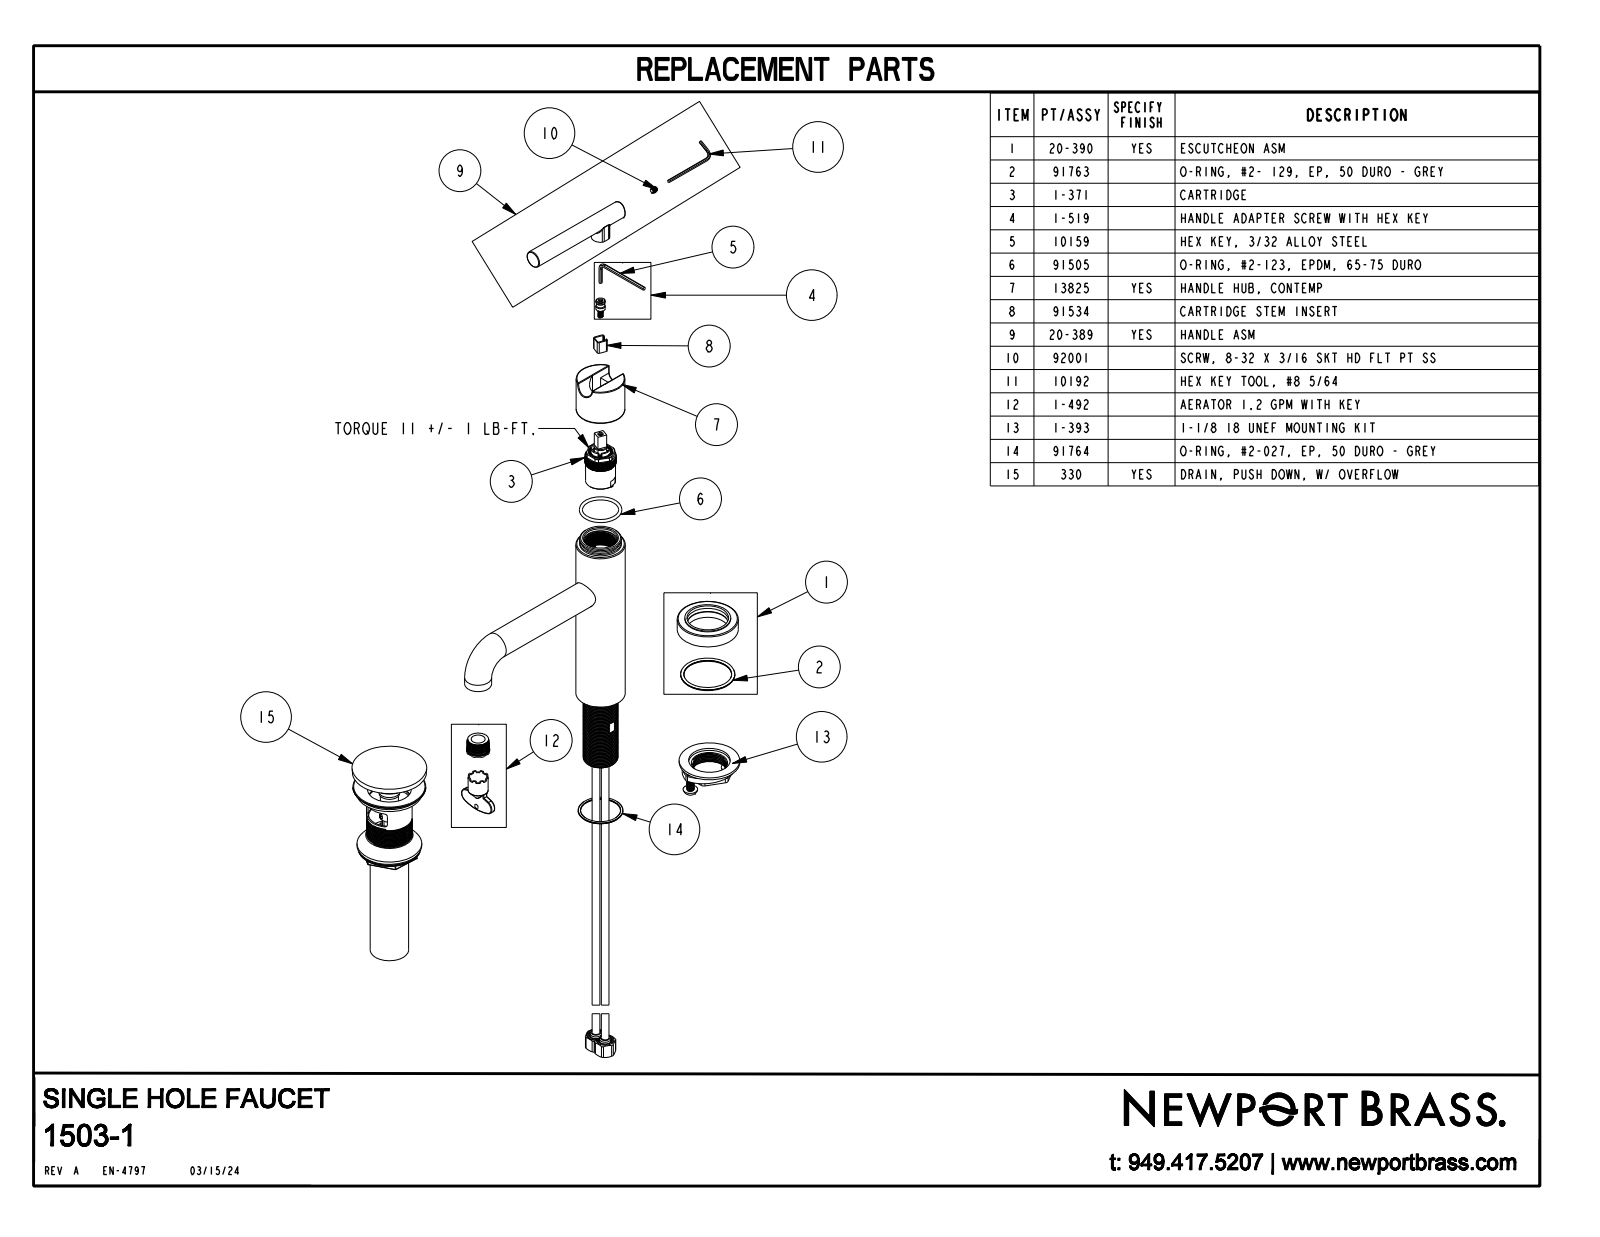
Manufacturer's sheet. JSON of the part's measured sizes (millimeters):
{"part_name": "1503-1_SW0001", "step_written_by": "CREO PARAMETRIC BY PTC INC, 2023134 (CONFIG_CONTROL_DESIGN)", "units": "millimeters", "bodies": {"solids": 1, "faces": 132, "planar": 46, "cylindrical": 54, "other": 32}, "overall_size": [200.3, 178.9, 50.3], "volume_mm3": 322300, "surface_area_mm2": 44750, "round_holes": [[14.2, 1], [22.4, 1]], "round_bosses_or_shafts": [[22.2, 2], [50.3, 1], [40.6, 1], [40.1, 1], [38.4, 1], [19.1, 1], [14.2, 1]], "partial_cylinders_radius": [[0.5, 6], [3, 4], [8, 4], [1.5, 2], [7.5, 1], [22.9, 1]], "face_to_face_distances": [10.8, 193.5, 182.7, 15.9, 177.8, 167, 15.7, 91, 80.2, 86.8]}
